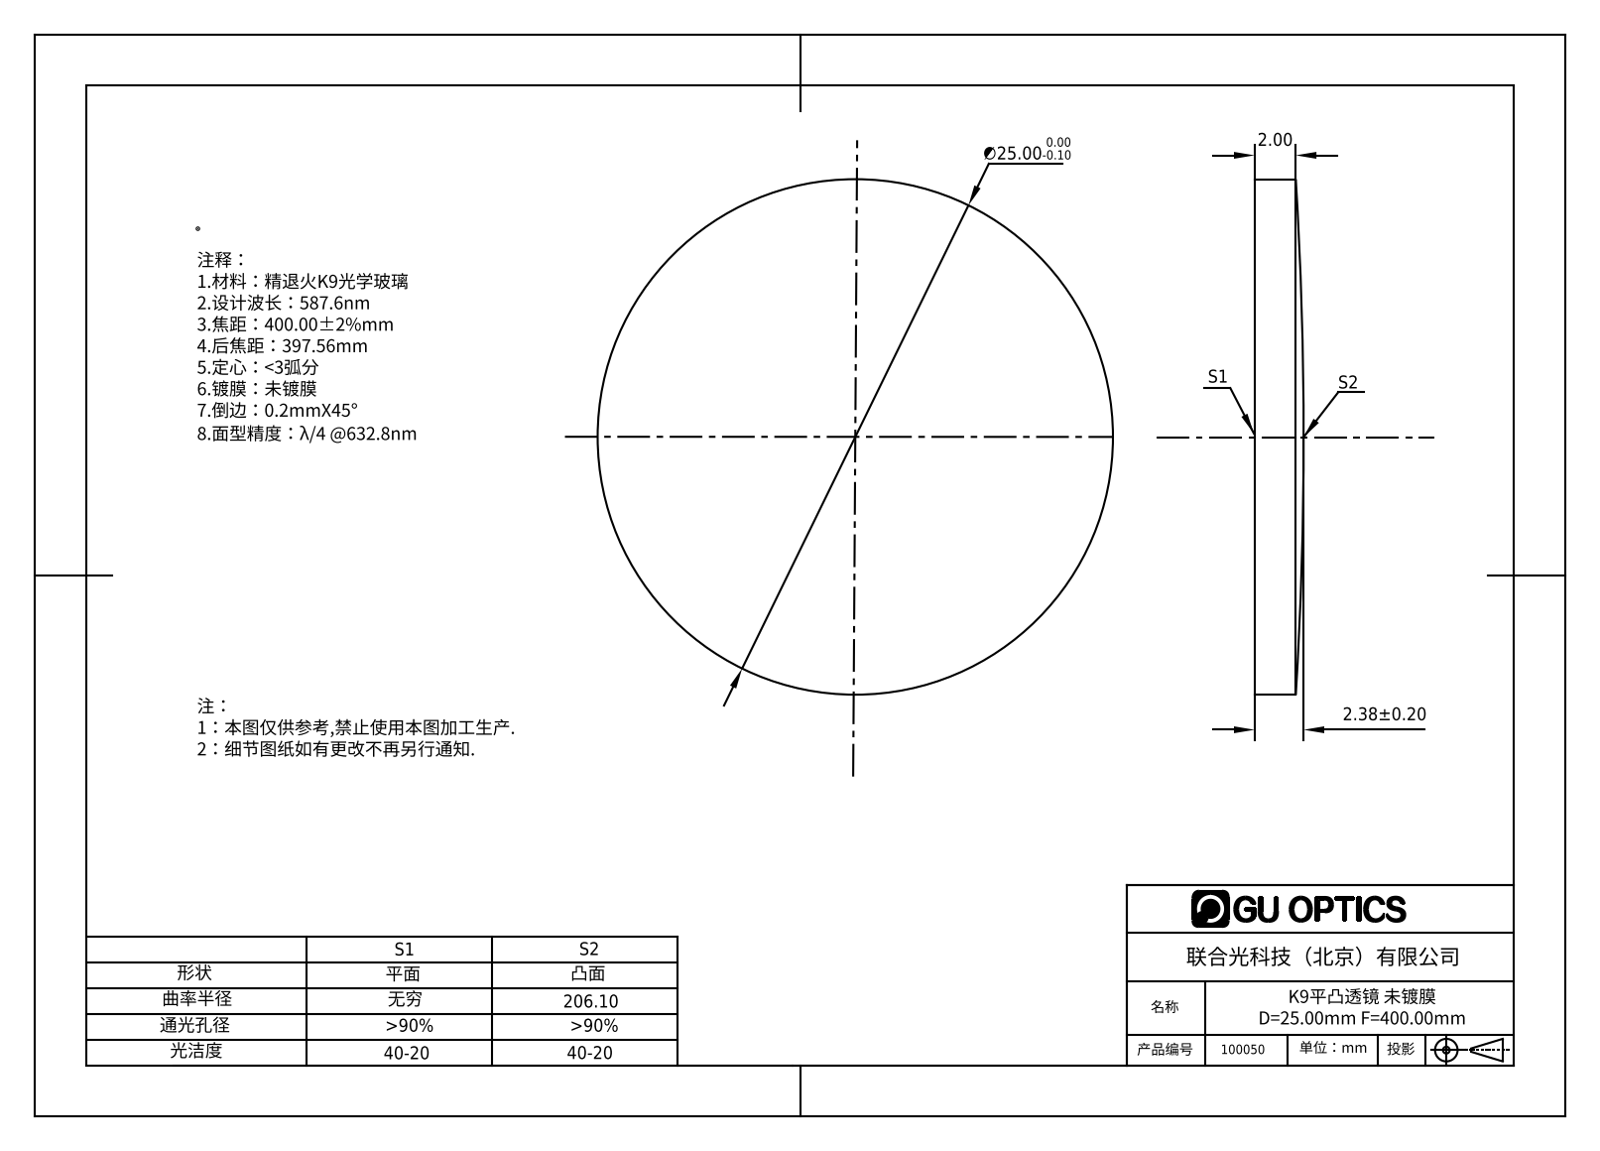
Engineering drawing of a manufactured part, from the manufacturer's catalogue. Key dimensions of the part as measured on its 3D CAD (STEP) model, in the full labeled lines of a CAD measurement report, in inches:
Part name (STEP PRODUCT): 100050
STEP written by: SolidWorks 2016 (AUTOMOTIVE_DESIGN)
Units: inches
Bodies: 1 solid, 5 faces (1 planar, 2 cylindrical, 2 other)
Overall size (bounding box): 0.984 × 0.984 × 0.094
Volume: 0.066 in³ · Surface area: 1.765 in²
Round bosses / shafts (diameter × count): ⌀0.984 ×1
